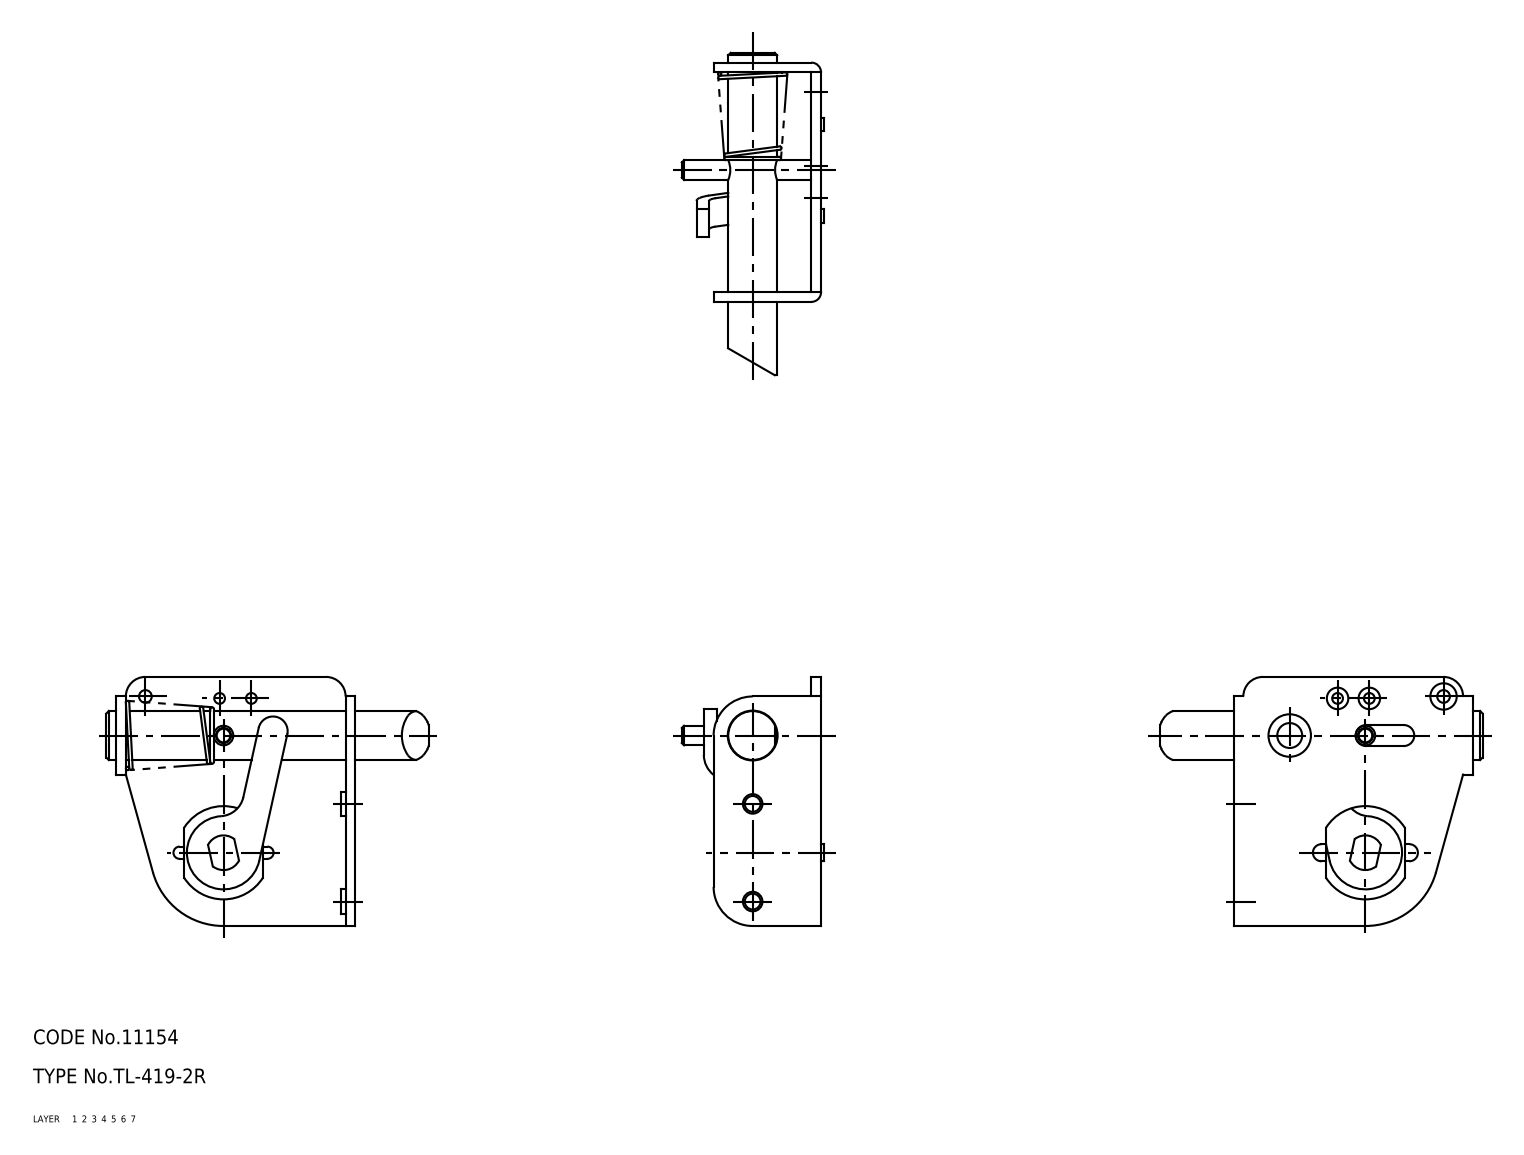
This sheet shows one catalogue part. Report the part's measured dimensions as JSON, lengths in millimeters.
{"part_name": "カム; TL-419-2R組立; TL_419_2R", "step_written_by": "SolidWorks 2015 (AUTOMOTIVE_DESIGN)", "units": "millimeters", "bodies": {"solids": 2, "faces": 163, "planar": 50, "cylindrical": 82, "other": 31}, "overall_size": [66, 51, 29.2], "volume_mm3": 11773, "surface_area_mm2": 11226, "round_holes": [[2.2, 2], [3.25, 2], [2.6, 1], [2.8, 1], [5.1, 1], [10.2, 1]], "round_bosses_or_shafts": [[5, 2], [14.2, 1], [10, 1], [4, 1]], "partial_cylinders_radius": [[2, 3], [0.3, 2], [1.25, 2], [1.75, 2], [2.15, 2], [2.6, 2], [4, 2], [5.2, 2]], "face_to_face_distances": [2, 47, 49, 2.6, 45, 15, 13, 17.6, 15.6, 7], "hole_center_spacings": [6.5, 7.63, 9.59, 12.4, 14, 15.21, 15.65, 17.75]}
